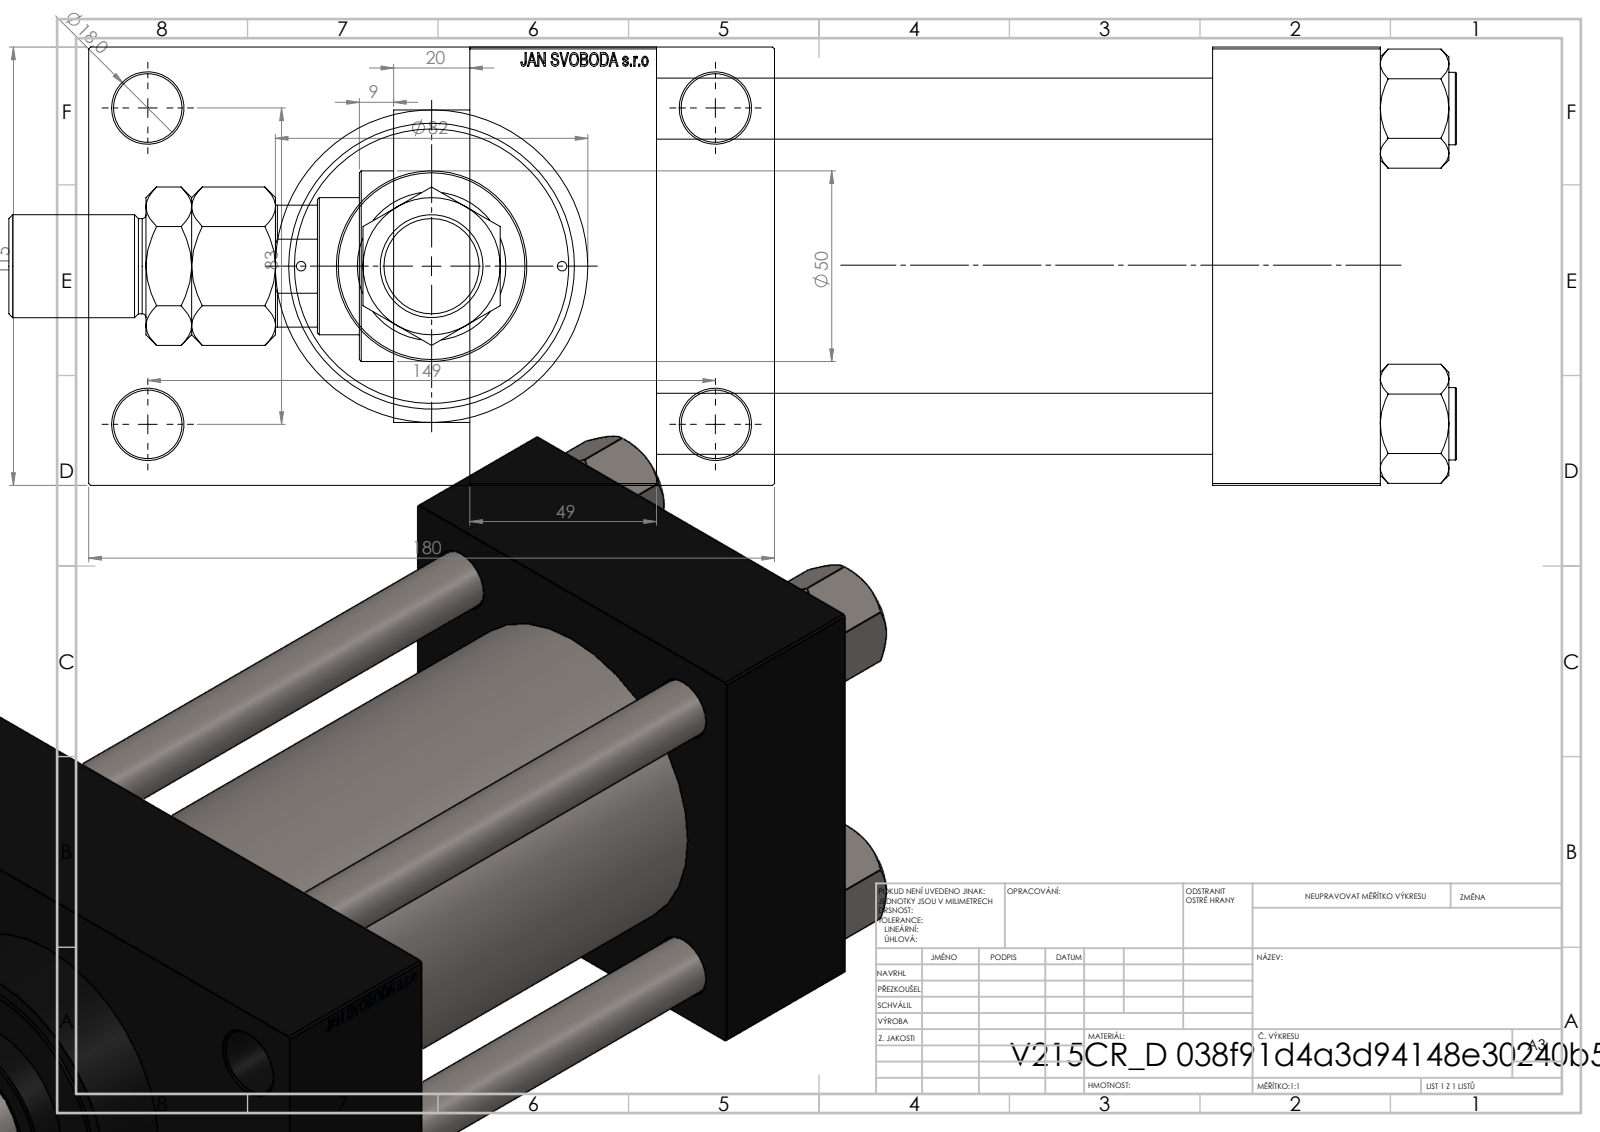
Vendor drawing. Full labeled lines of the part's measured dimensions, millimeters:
Part name (STEP PRODUCT): NUT_M5_D; V215CR_D_Body; V215_VC_A; V215CR_VCP_D (+2 more)
STEP written by: SolidWorks 2019 (CONFIG_CONTROL_DESIGN)
Units: millimetres
Bodies: 12 solids, 1208 faces (562 planar, 96 cylindrical, 550 other)
Overall size (bounding box): 380 × 180 × 115
Volume: 2 246 000 mm³ · Surface area: 372 790 mm²
Round holes (diameter × count): ⌀16 ×4, ⌀18 ×4, ⌀2.5 ×2, ⌀7 ×2, ⌀26.44 ×2, ⌀35 ×2, ⌀25.5 ×1, ⌀36 ×1, ⌀39 ×1, ⌀61 ×1, ⌀72 ×1, ⌀80 ×1
Round bosses / shafts (diameter × count): ⌀19 ×4, ⌀86 ×1, ⌀82 ×1, ⌀50 ×1, ⌀27 ×1, ⌀25 ×1
Partial cylindrical surfaces — rounded edges, fillets, slot ends (radius × count): R17.5 ×1
Main face-to-face distances: 115, 146, 195, 49, 44, 190, 239, 32.5, 147.5, 100
Hole centre spacings: 33.15, 41.96, 57.81, 58.48, 82.7, 85.28, 86.17, 89.24
